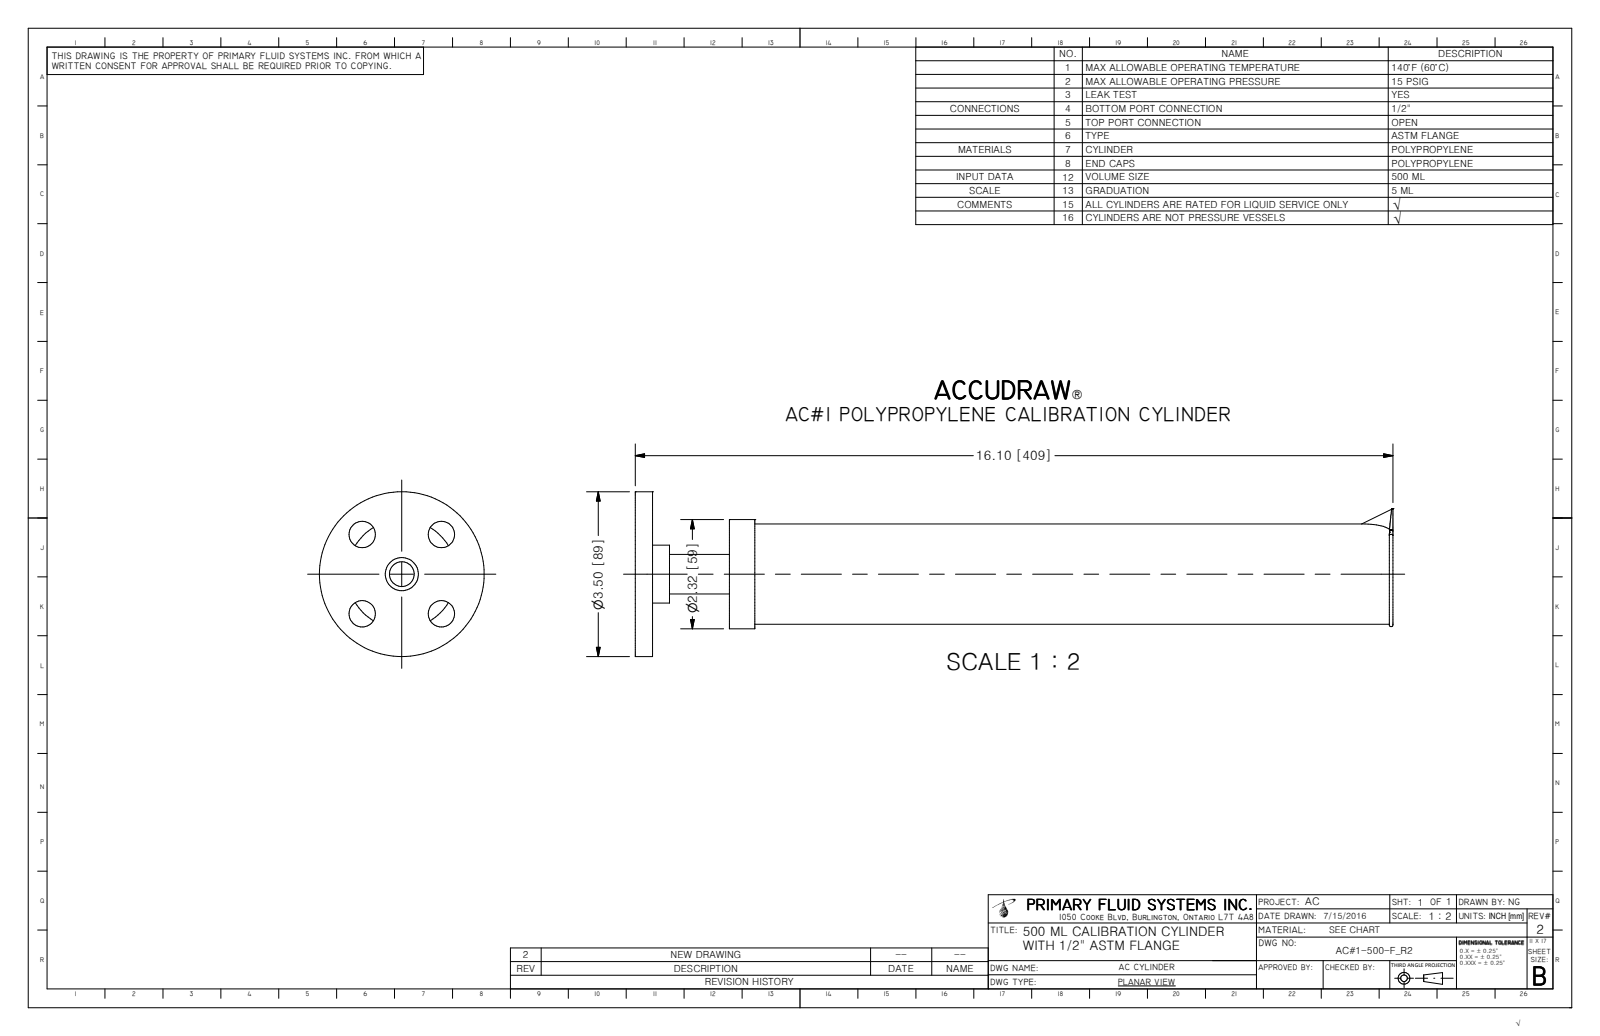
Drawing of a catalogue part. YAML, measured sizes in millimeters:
part_name: "AC#1-500-F_R2; SA-50FLG-PP_R0; FLG-50PP_R0; PIPE-50PP-SCH80 (+2 more)"
step_written_by: "Autodesk Inventor 2009 (AUTOMOTIVE_DESIGN)"
units: millimeters
bodies: {solids: 4, faces: 40, planar: 17, cylindrical: 15, other: 8}
overall_size: [408.9, 88.9, 88.9]
volume: 225200
surface_area: 147400
round_holes:
  - {diameter: 14.2, count: 4}
  - {diameter: 13.4, count: 1}
  - {diameter: 17.5, count: 1}
  - {diameter: 17.9, count: 1}
  - {diameter: 21.3, count: 1}
  - {diameter: 49.9, count: 1}
round_bosses_or_shafts:
  - {diameter: 88.9, count: 1}
  - {diameter: 58.9, count: 1}
  - {diameter: 54.1, count: 1}
  - {diameter: 47, count: 1}
  - {diameter: 31.2, count: 1}
face_to_face_distances: [9.3, 50.8, 41.5, 69.9, 60.6, 19.1, 64.5, 55.2, 13.7, 5.3]
hole_center_spacings: [30.2, 42.7, 30.2, 30.2, 60.5]
